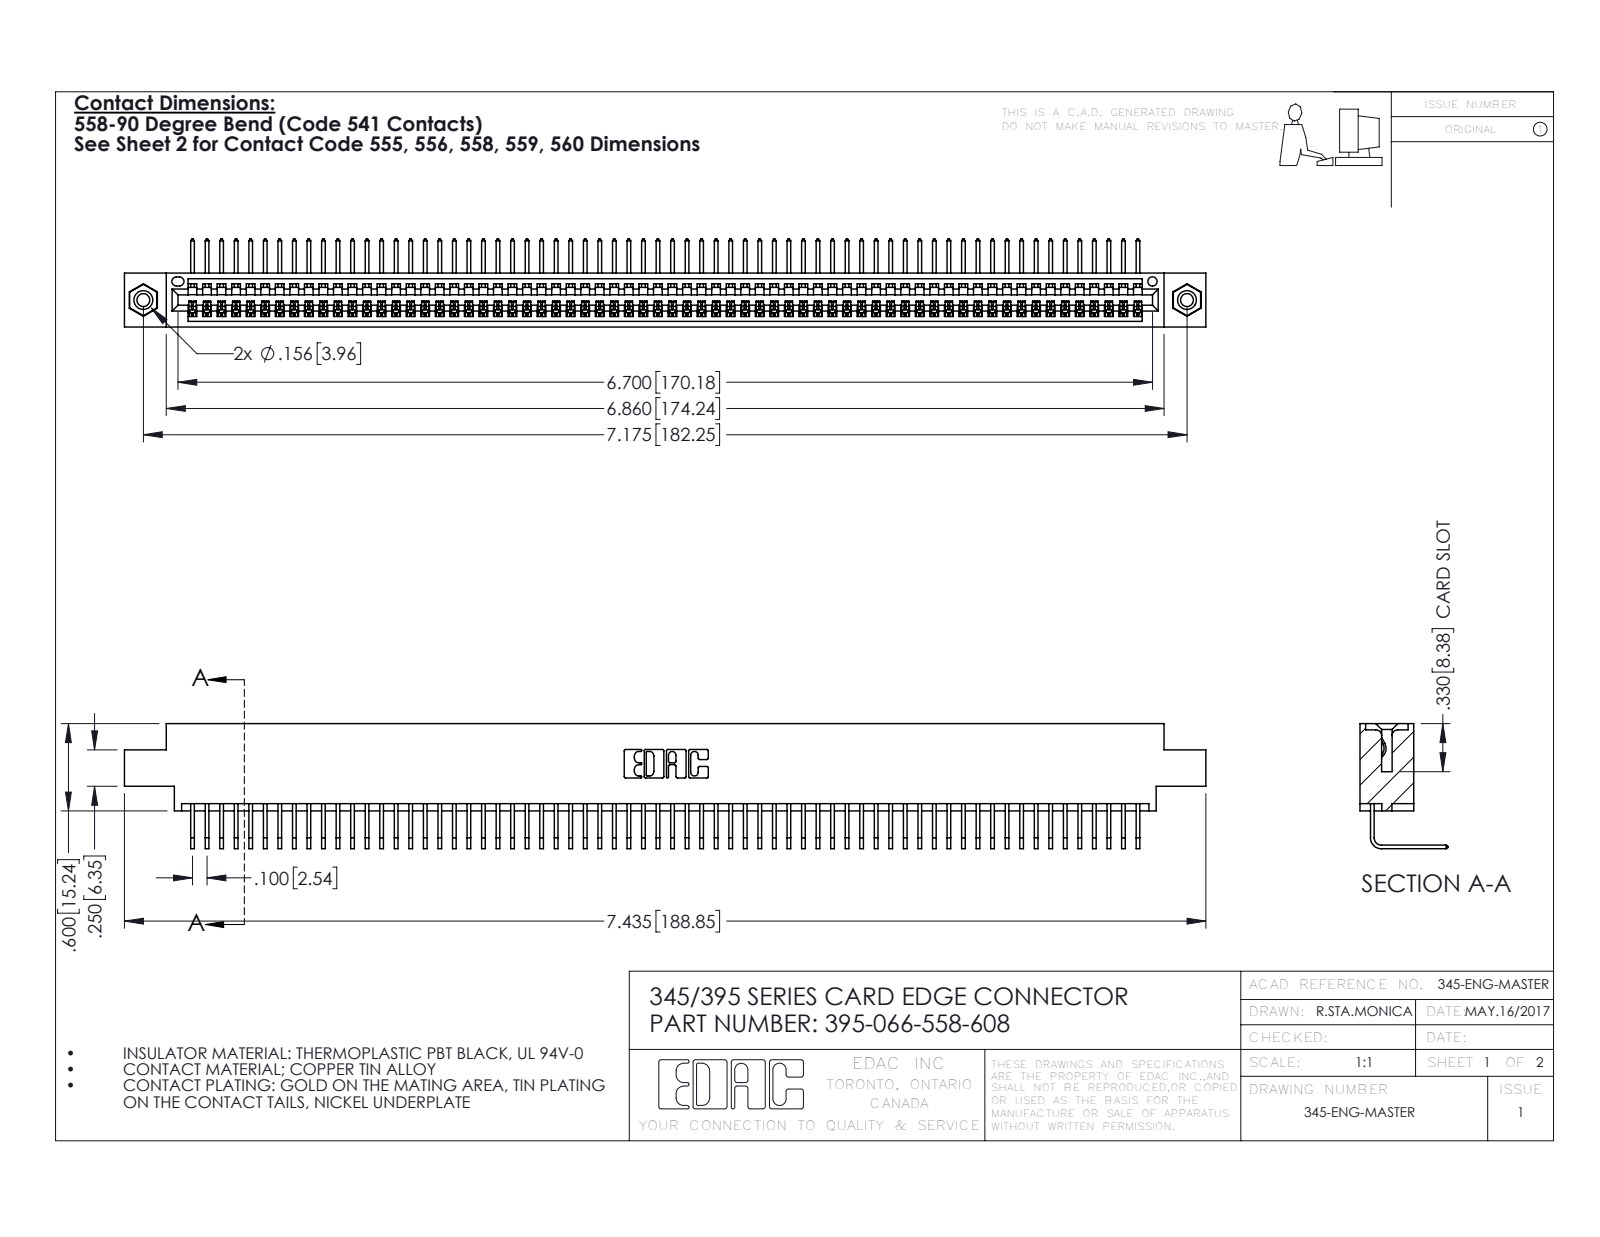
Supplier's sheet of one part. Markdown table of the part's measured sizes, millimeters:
| quantity | value |
| --- | --- |
| part name | 345 Part_0.170 Offset - 0.156 Dia-TI; 345-250-001_345-250-003-102; 345-292-001_558 Tail - 2; 395-066-558-608 |
| STEP written by | SolidWorks 2016 (CONFIG_CONTROL_DESIGN) |
| units | millimeters |
| bodies | 69 solids, 4150 faces (2888 planar, 1246 cylindrical, 16 other) |
| overall size | 188.8 × 21.8 × 15.4 |
| volume | 18 240 mm³ |
| surface area | 25 990 mm² |
| round holes (diameter × count) | 2.3 × 2, 3.2 × 2, 4 × 2, 1.6 × 1 |
| round bosses / shafts (diameter × count) | 3.9 × 2 |
| partial cylindrical surfaces (radius × count) | 0.2 × 132, 0.3 × 22, 0.2 × 6, 0.8 × 6, 0.7 × 3, 0.8 × 2, 1 × 2, 0.4 × 1 |
| main face-to-face distances | 1.8, 7.6, 9.4, 5.1, 2.5, 6.9, 0.6, 5.7, 4.4, 3.8 |
| hole center spacings | 6.9, 176.3, 182.2 |
